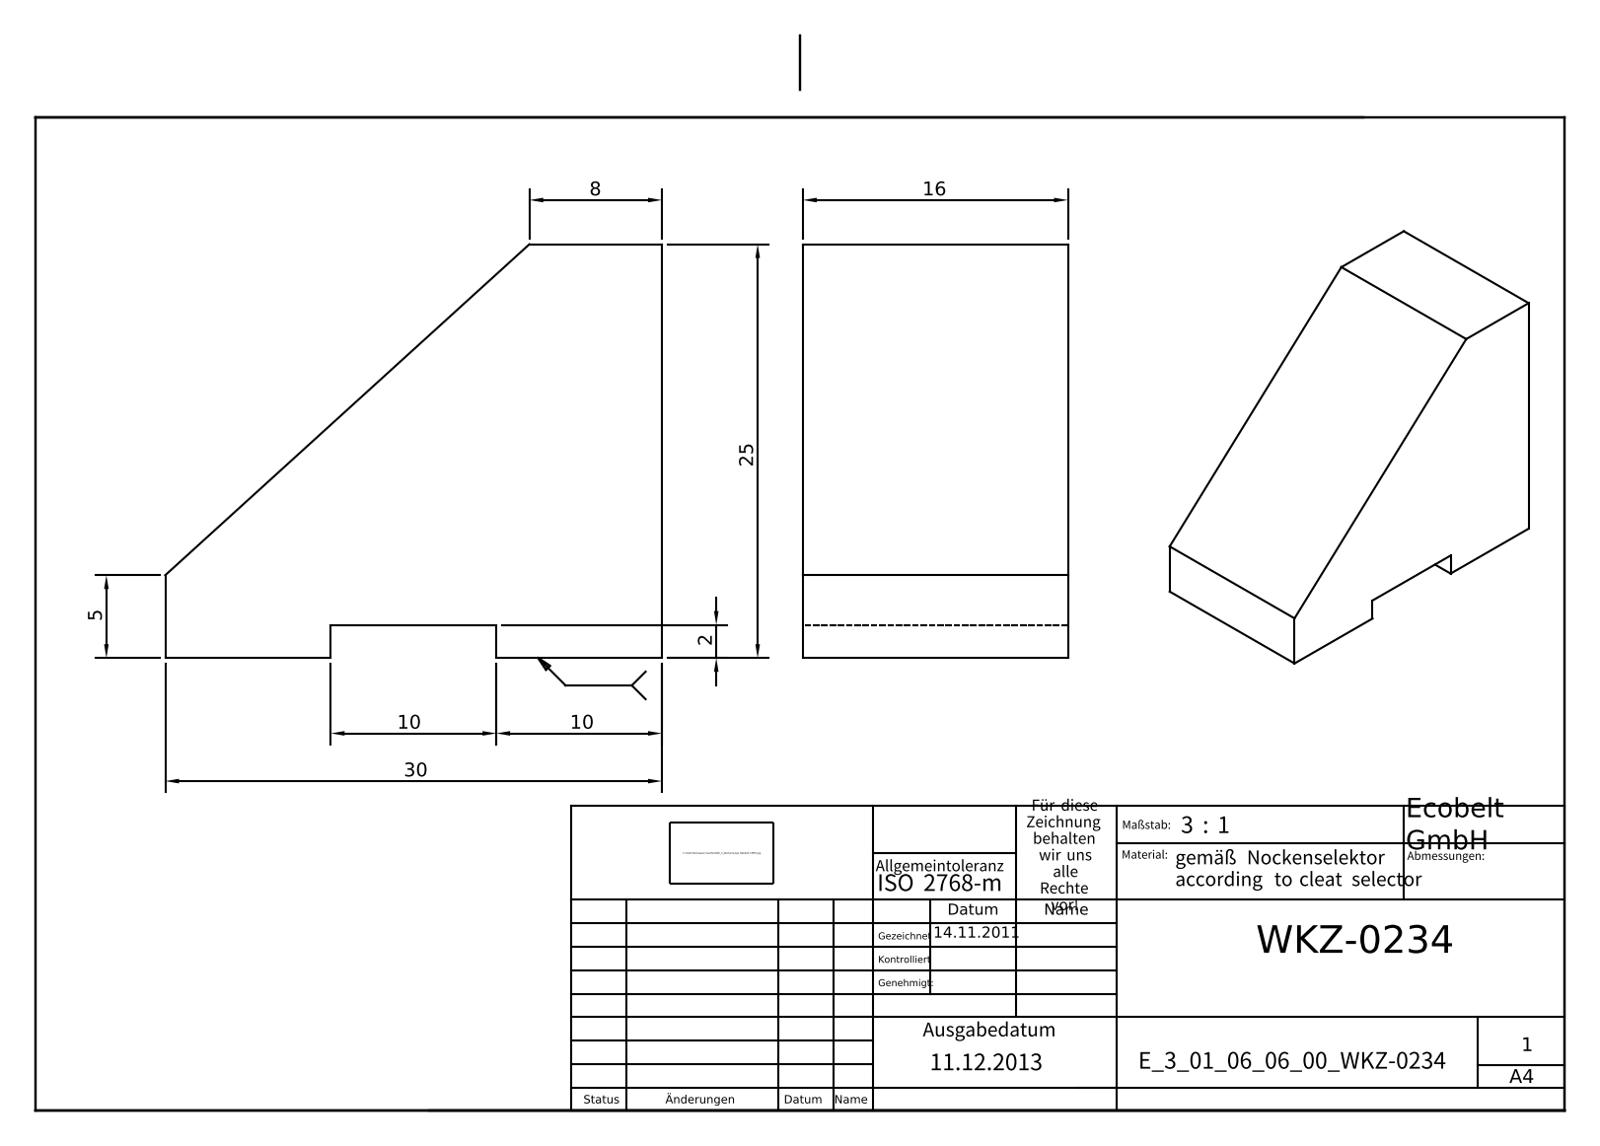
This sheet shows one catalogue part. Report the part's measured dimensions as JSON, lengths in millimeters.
{"part_name": "E_3_01_06_06_00_WKZ-0234", "step_written_by": "Autodesk Inventor 2025 (AUTOMOTIVE_DESIGN)", "units": "millimeters", "bodies": {"solids": 1, "faces": 11, "planar": 11, "cylindrical": 0, "other": 0}, "overall_size": [30, 25, 16], "volume_mm3": 8160, "surface_area_mm2": 2648, "face_to_face_distances": [16, 2, 25, 23, 10, 30, 20]}
